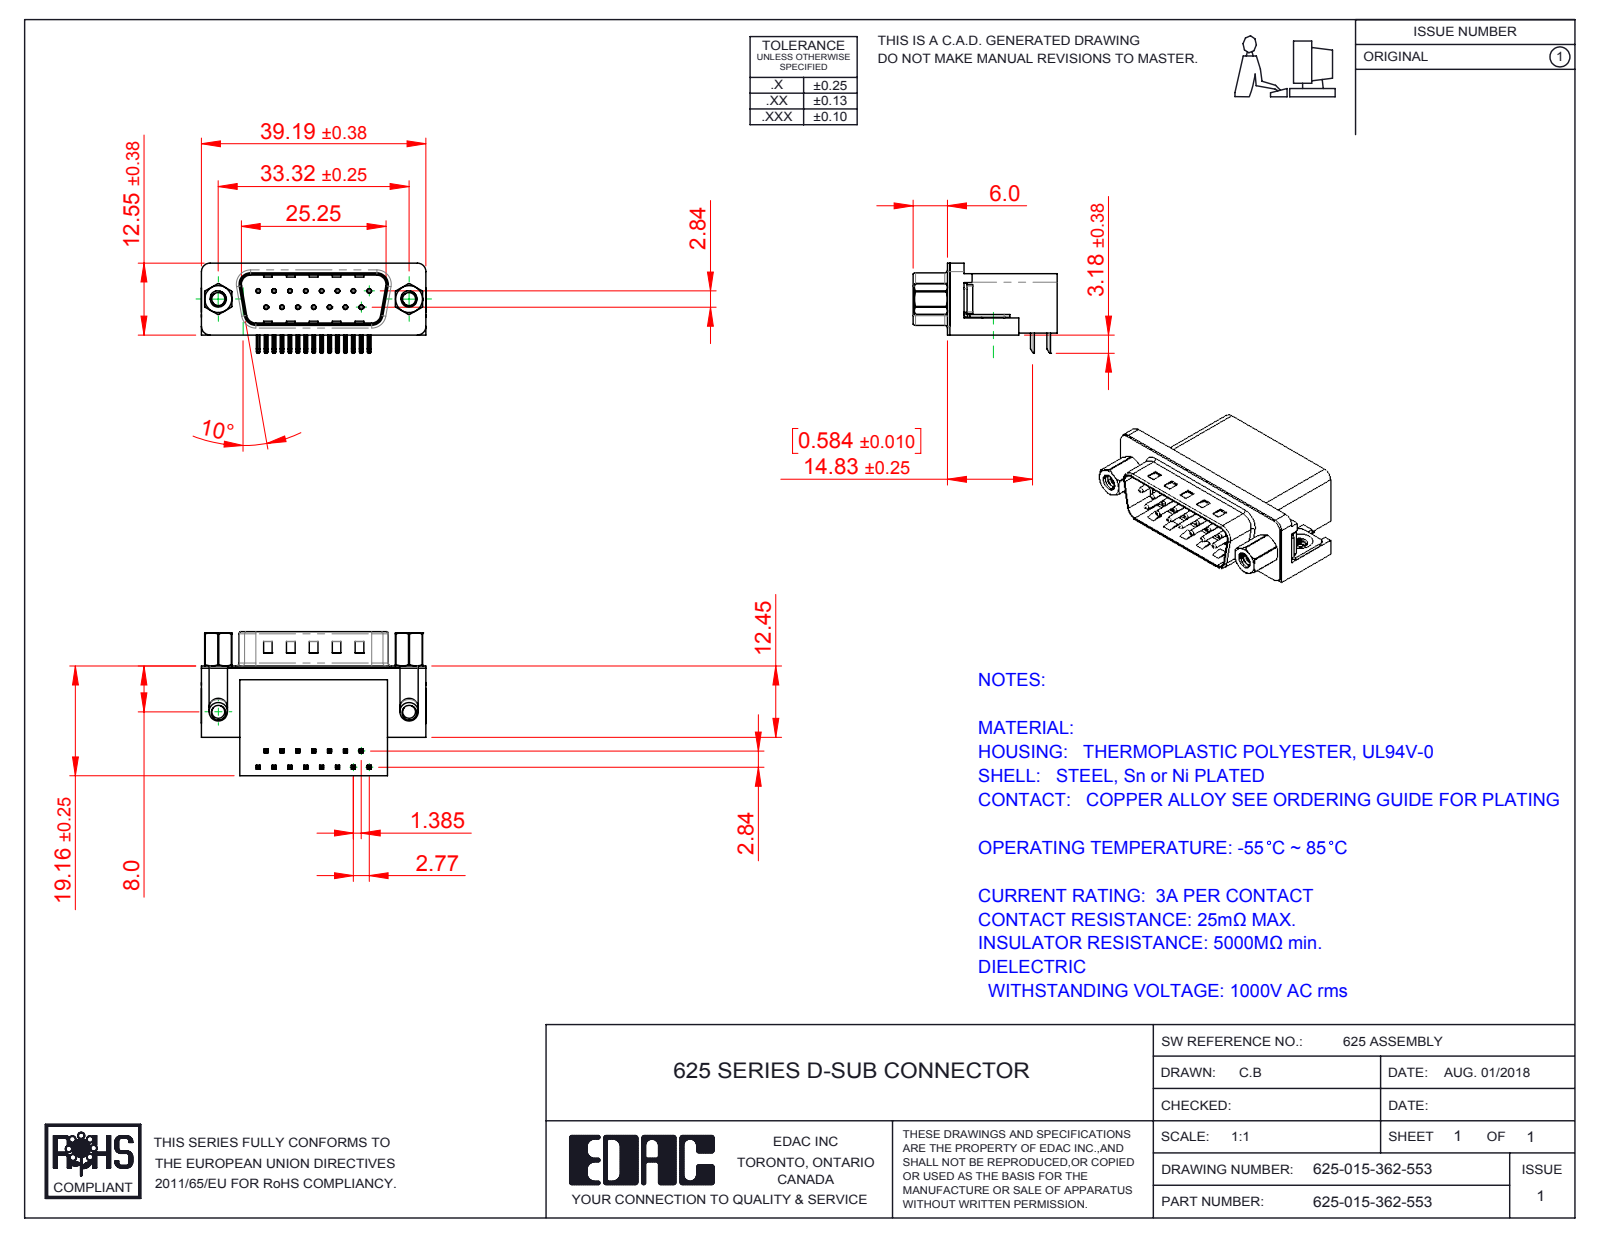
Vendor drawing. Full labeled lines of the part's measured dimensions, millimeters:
Part name (STEP PRODUCT): 625 Housing_15 Socket; 625 4-40 Hex Standoff 5; 625 4-40 Threaded Board Mount; 625 Shell_15 Socket (+4 more)
STEP written by: SolidWorks 2016 (CONFIG_CONTROL_DESIGN)
Units: millimetres
Bodies: 23 solids, 1637 faces (917 planar, 531 cylindrical, 189 other)
Overall size (bounding box): 39.22 × 25.16 × 15.73
Volume: 6 467 mm³ · Surface area: 6 987 mm²
Round holes (diameter × count): ⌀0.35 ×15, ⌀0.8 ×15, ⌀2.26 ×4, ⌀2.29 ×2, ⌀4 ×2, ⌀4.8 ×2, ⌀5 ×2
Round bosses / shafts (diameter × count): ⌀0.75 ×15, ⌀4.9 ×2, ⌀4.75 ×2, ⌀3.9 ×2, ⌀3.26 ×2, ⌀2.79 ×2
Partial cylindrical surfaces — rounded edges, fillets, slot ends (radius × count): R0.25 ×68, R0.12 ×30, R1 ×16, R0.5 ×9, R1.6 ×8, R1.5 ×6, R0.9 ×4, R2 ×4
Main face-to-face distances: 0.4, 10.35, 18.76, 2.1, 19.16, 10.46, 1.7, 10.86, 8.76, 16.26
Hole centre spacings: 3.16, 2.77, 5.54, 8.31, 11.08, 5.03, 5.04, 7.48
